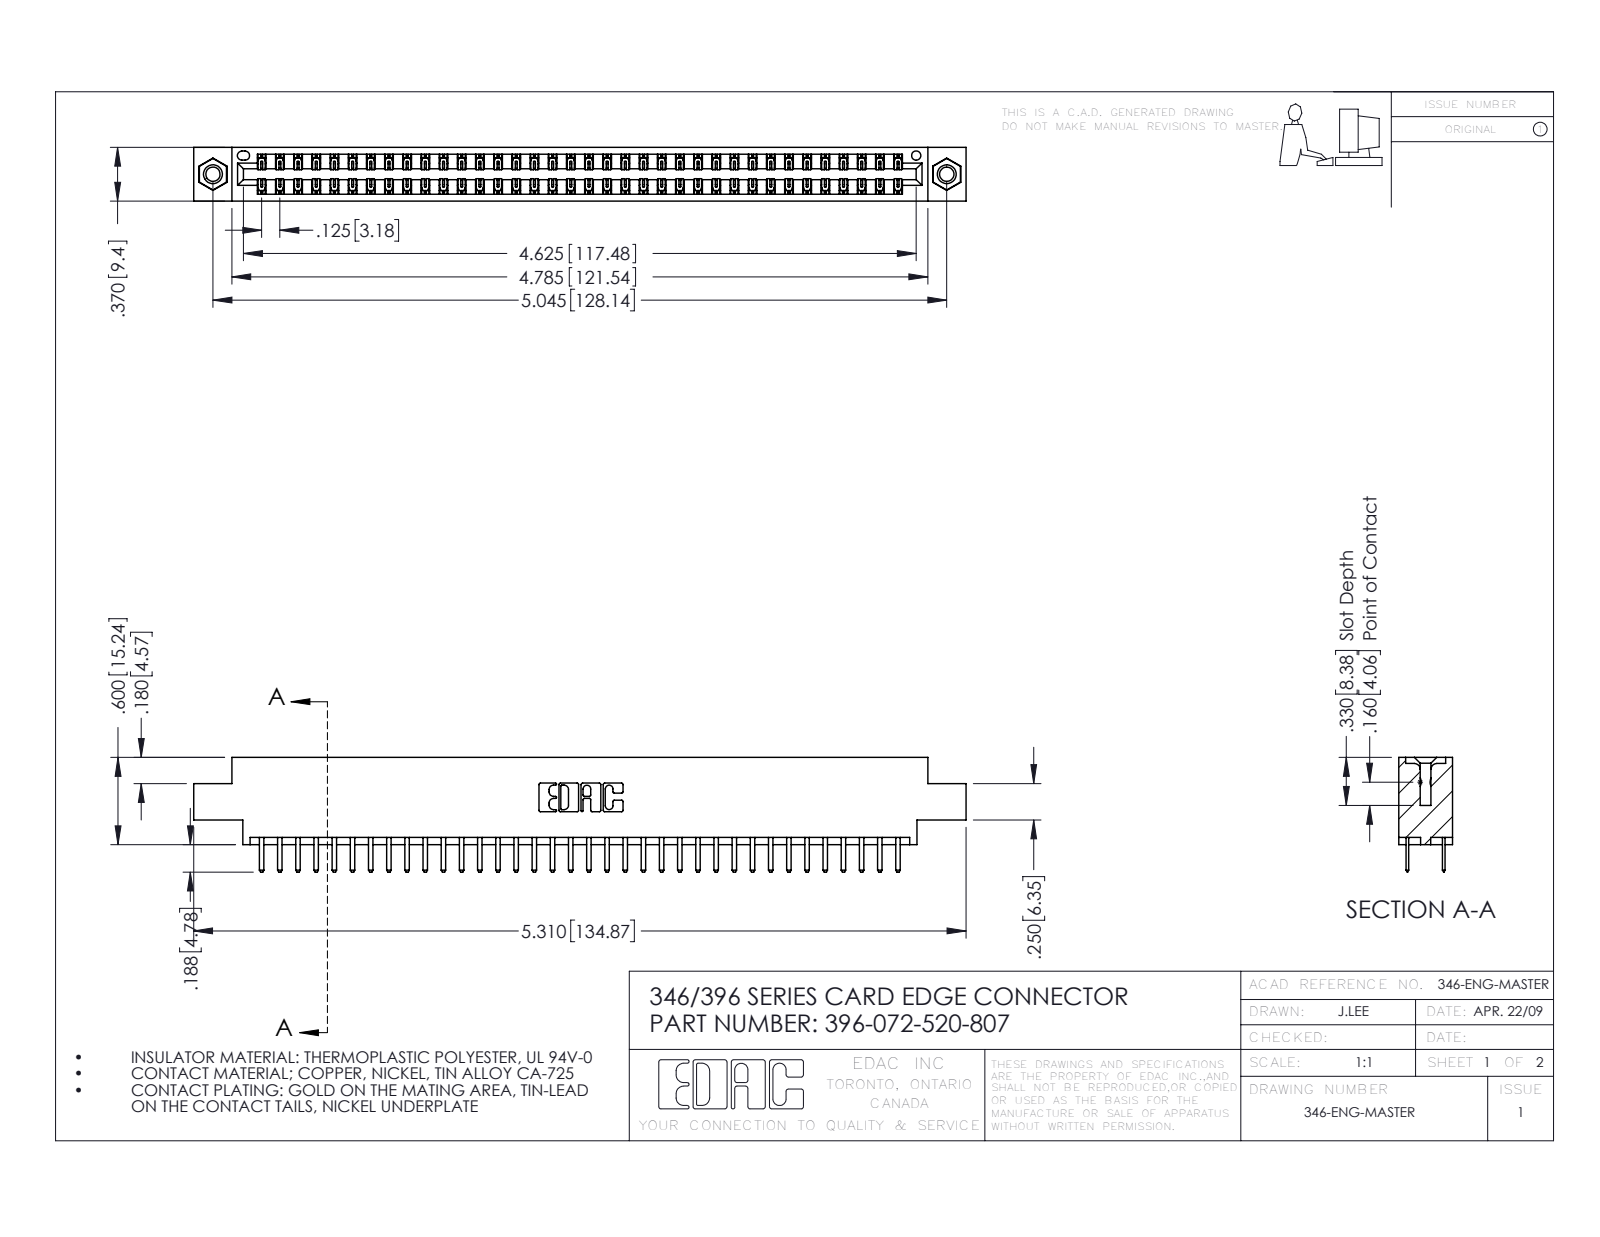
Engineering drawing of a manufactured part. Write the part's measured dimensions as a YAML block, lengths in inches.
part_name: "345-292-001_345-293-120; 396-072-520-807; 345-250-001_345-250-005-103; 346 Part_0.170 Offset - 0.156 Dia-TI"
step_written_by: "SolidWorks 2016 (CONFIG_CONTROL_DESIGN)"
units: inches
bodies: {solids: 75, faces: 4218, planar: 2776, cylindrical: 1426, other: 16}
overall_size: [5.31, 0.788, 0.37]
volume: 0.788
surface_area: 27.57
round_holes:
  - {diameter: 0.098, count: 2}
  - {diameter: 0.125, count: 2}
  - {diameter: 0.156, count: 2}
  - {diameter: 0.064, count: 1}
round_bosses_or_shafts:
  - {diameter: 0.155, count: 2}
partial_cylinders:
  - {radius: 0.006, count: 108}
  - {radius: 0.01, count: 76}
  - {radius: 0.01, count: 22}
  - {radius: 0.007, count: 6}
  - {radius: 0.031, count: 6}
  - {radius: 0.026, count: 3}
  - {radius: 0.014, count: 2}
  - {radius: 0.022, count: 2}
face_to_face_distances: [0.048, 0.322, 0.37, 0.25, 0.275, 0.072, 0.298, 0.025, 0.222, 0.148]
hole_center_spacings: [0.246, 4.836, 5.045]
